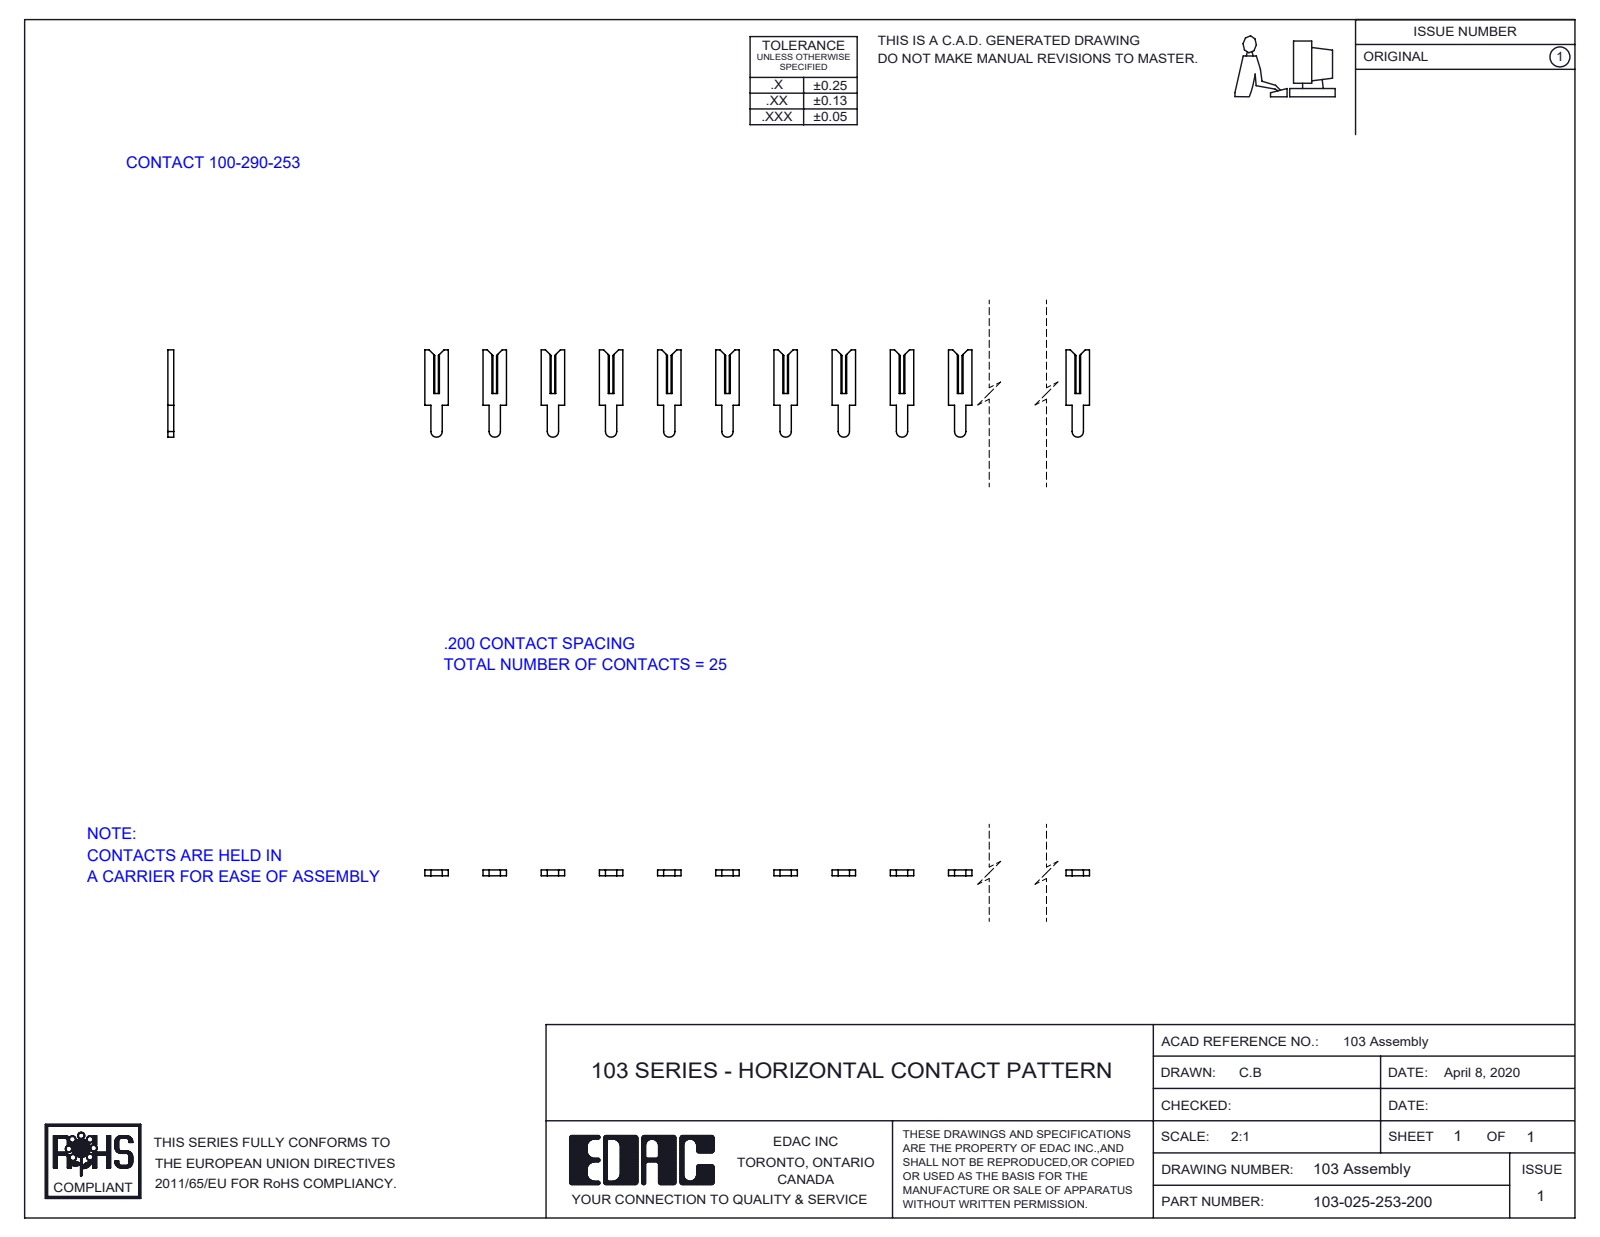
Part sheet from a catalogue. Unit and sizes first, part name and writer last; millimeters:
Units: millimetres
Overall size (bounding box): 124 × 7.6 × 0.5
Partial cylindrical surfaces — rounded edges, fillets, slot ends (radius × count): R0.5 ×25
Main face-to-face distances: 0.5, 5.1, 10.2, 3.6, 15.2, 21.5, 7.2, 20.3, 25.1, 18
Volume: 100 mm³ · Surface area: 860 mm²
Bodies: 25 solids, 500 faces (475 planar, 25 cylindrical, 0 other)
Part name (STEP PRODUCT): 103-025-253-200; 100-290-001_100-290-253
STEP written by: SolidWorks 2016 (CONFIG_CONTROL_DESIGN)
